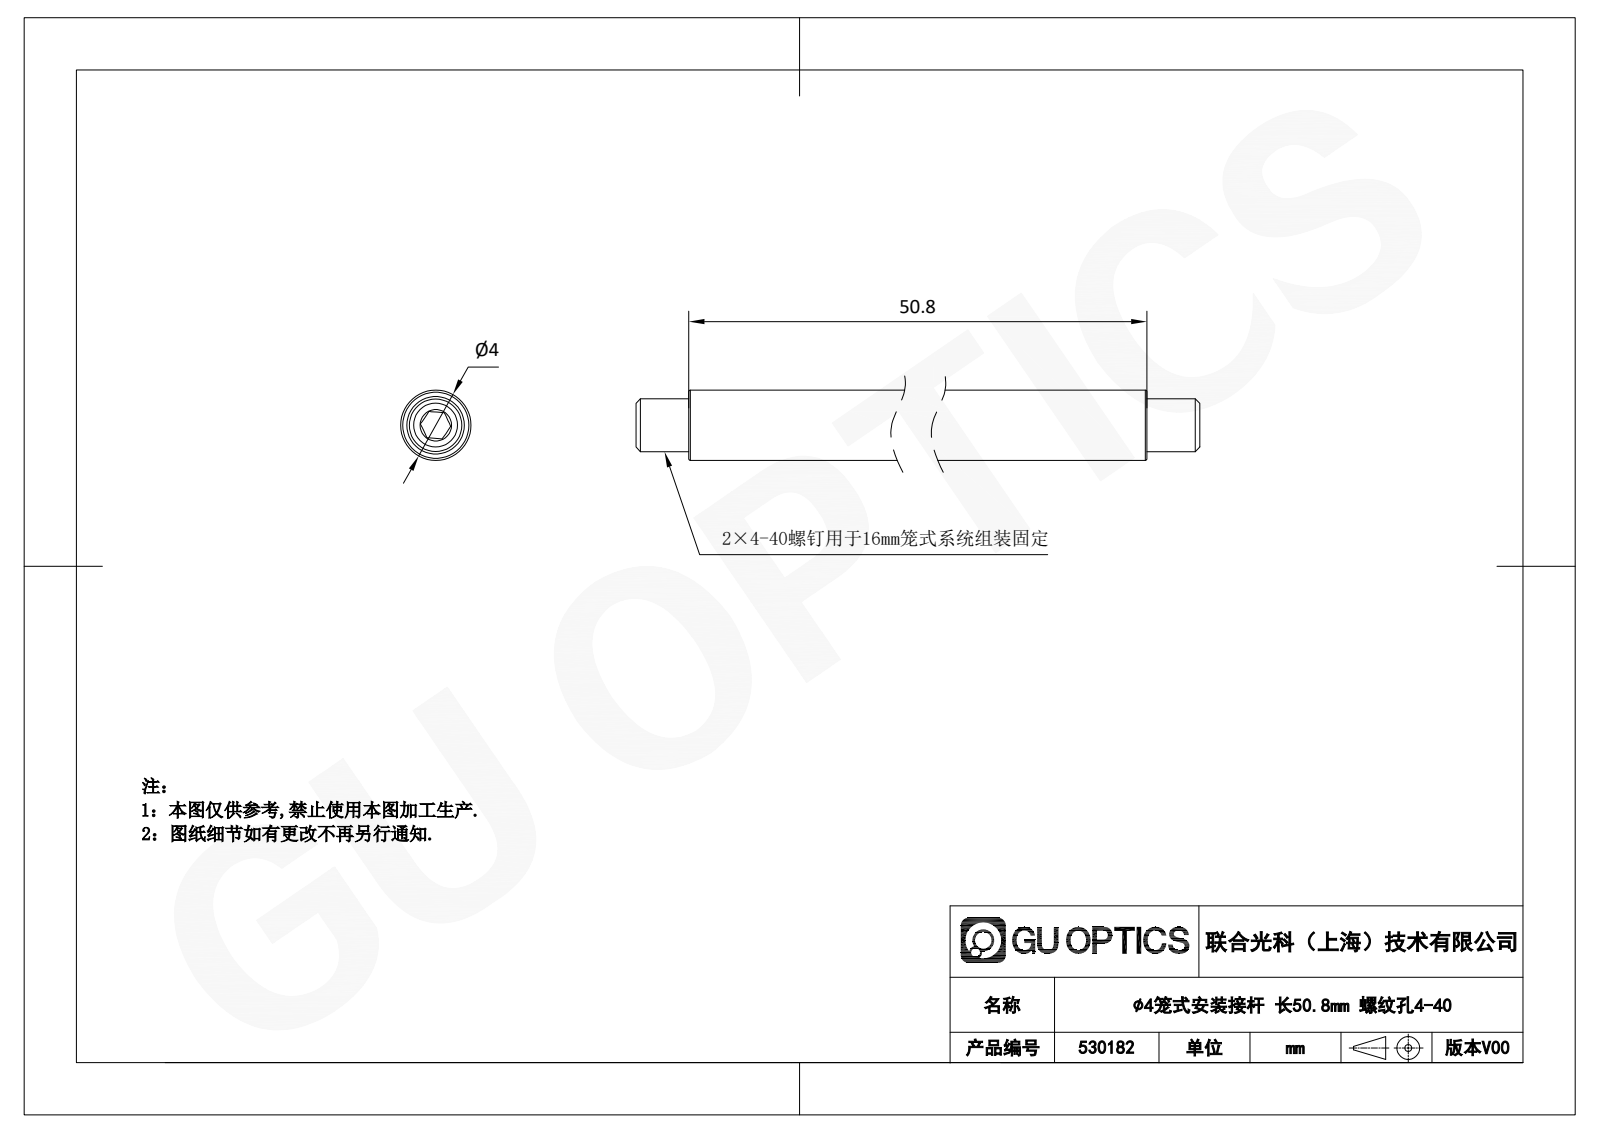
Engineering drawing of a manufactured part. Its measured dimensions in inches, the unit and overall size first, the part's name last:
Units: inches
Overall size (bounding box): 2.394 × 0.157 × 0.157
Round holes (diameter × count): ⌀0.098 ×1
Round bosses / shafts (diameter × count): ⌀0.157 ×1, ⌀0.118 ×1
Main face-to-face distances: 0.118, 1.882, 0.197, 0.315, 2.079, 2.197, 0.059, 2, 0.039, 2.354
Volume: 0.042 in³ · Surface area: 1.44 in²
Bodies: 3 solids, 37 faces (20 planar, 5 cylindrical, 12 other)
Part name (STEP PRODUCT): 530182
STEP written by: SolidWorks 2020 (CONFIG_CONTROL_DESIGN)
